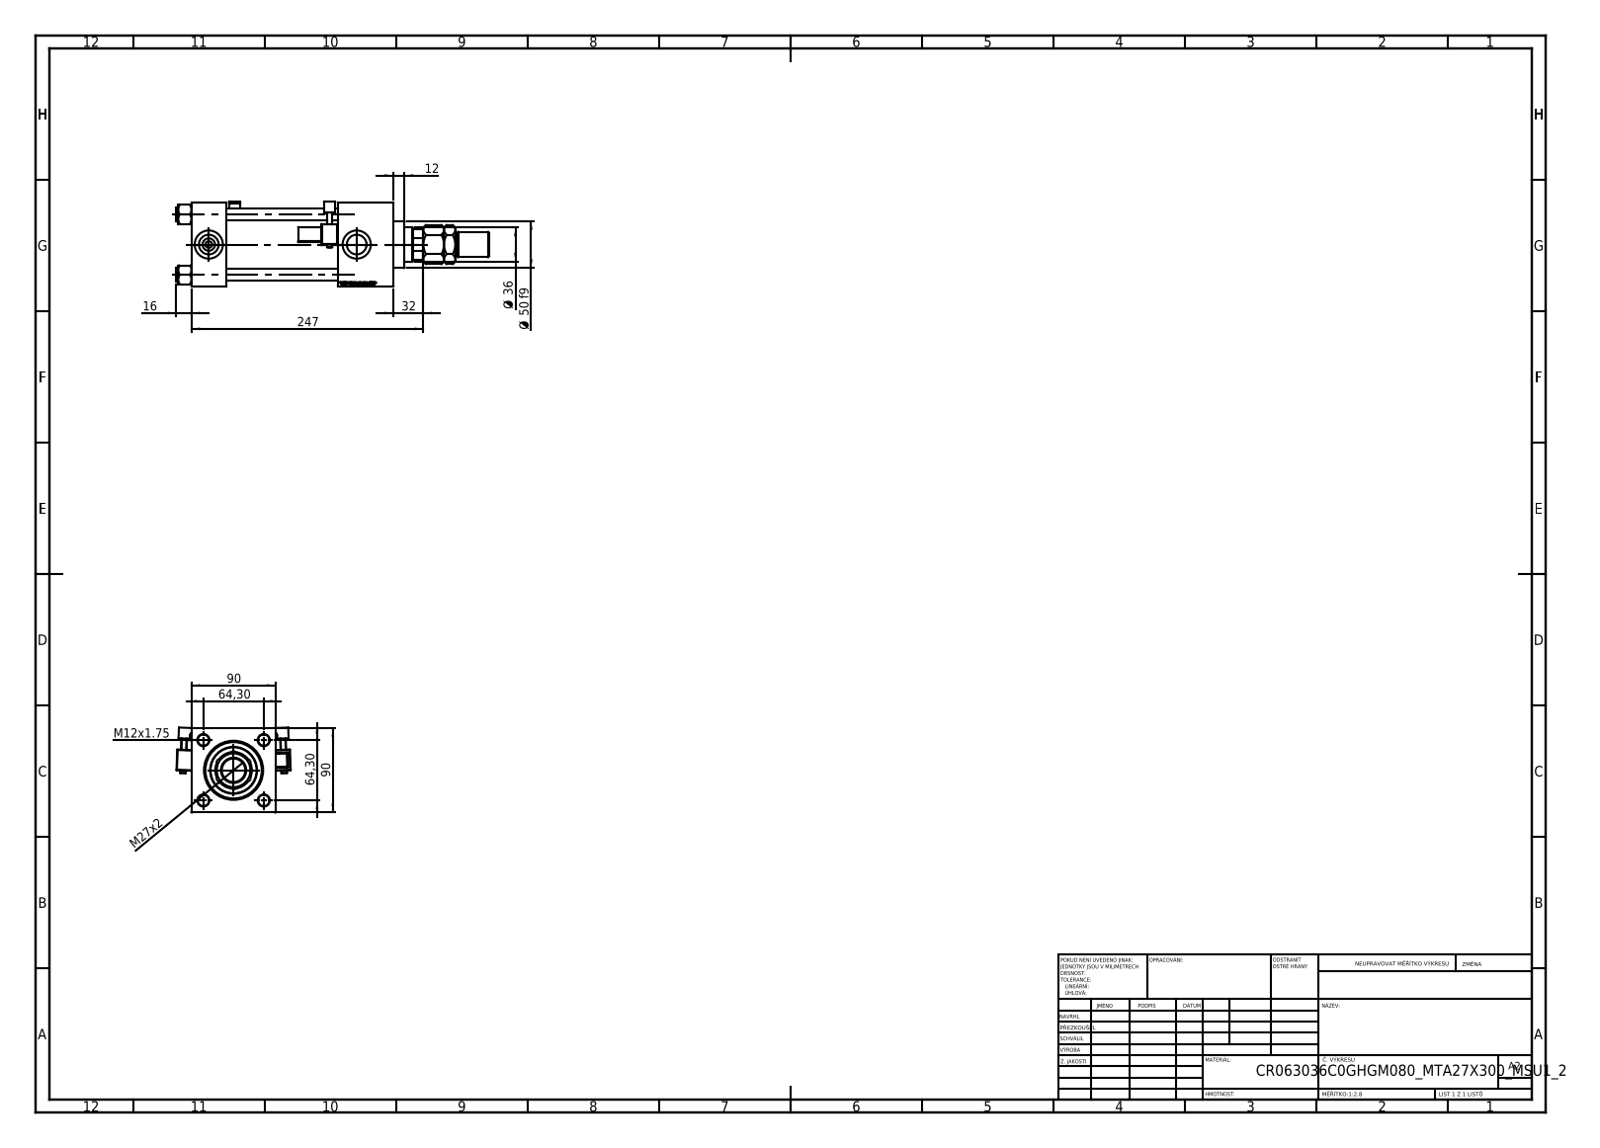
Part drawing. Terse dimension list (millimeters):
name: V215CR_VCP_C; NUT_M5_C; V215CR_C_TYCINKA; MTA (+3 more)
written by: SolidWorks 2019 (CONFIG_CONTROL_DESIGN)
unit: mm
bodies: 14 solids, 1351 faces (599 planar, 150 cylindrical, 602 other)
size: 333 × 121.57 × 90.53
volume: 1 193 000 mm³; area: 246 676 mm²
holes: 4× ⌀12, 2× ⌀7, 2× ⌀20.96, 2× ⌀30, 1× ⌀25.5, 1× ⌀36, 1× ⌀39, 1× ⌀50, 1× ⌀60, 1× ⌀63
bosses: 4× ⌀15, 2× ⌀6, 1× ⌀69, 1× ⌀27, 1× ⌀25
rounds: 48× R0.5, 2× R1, 2× R2.5, 2× R4, 1× R17.5
face distances: 90, 37, 156, 119, 59, 215, 178, 186.3, 149.3, 30.3
hole spacings: 45.47, 64.3, 90.93, 157.5
